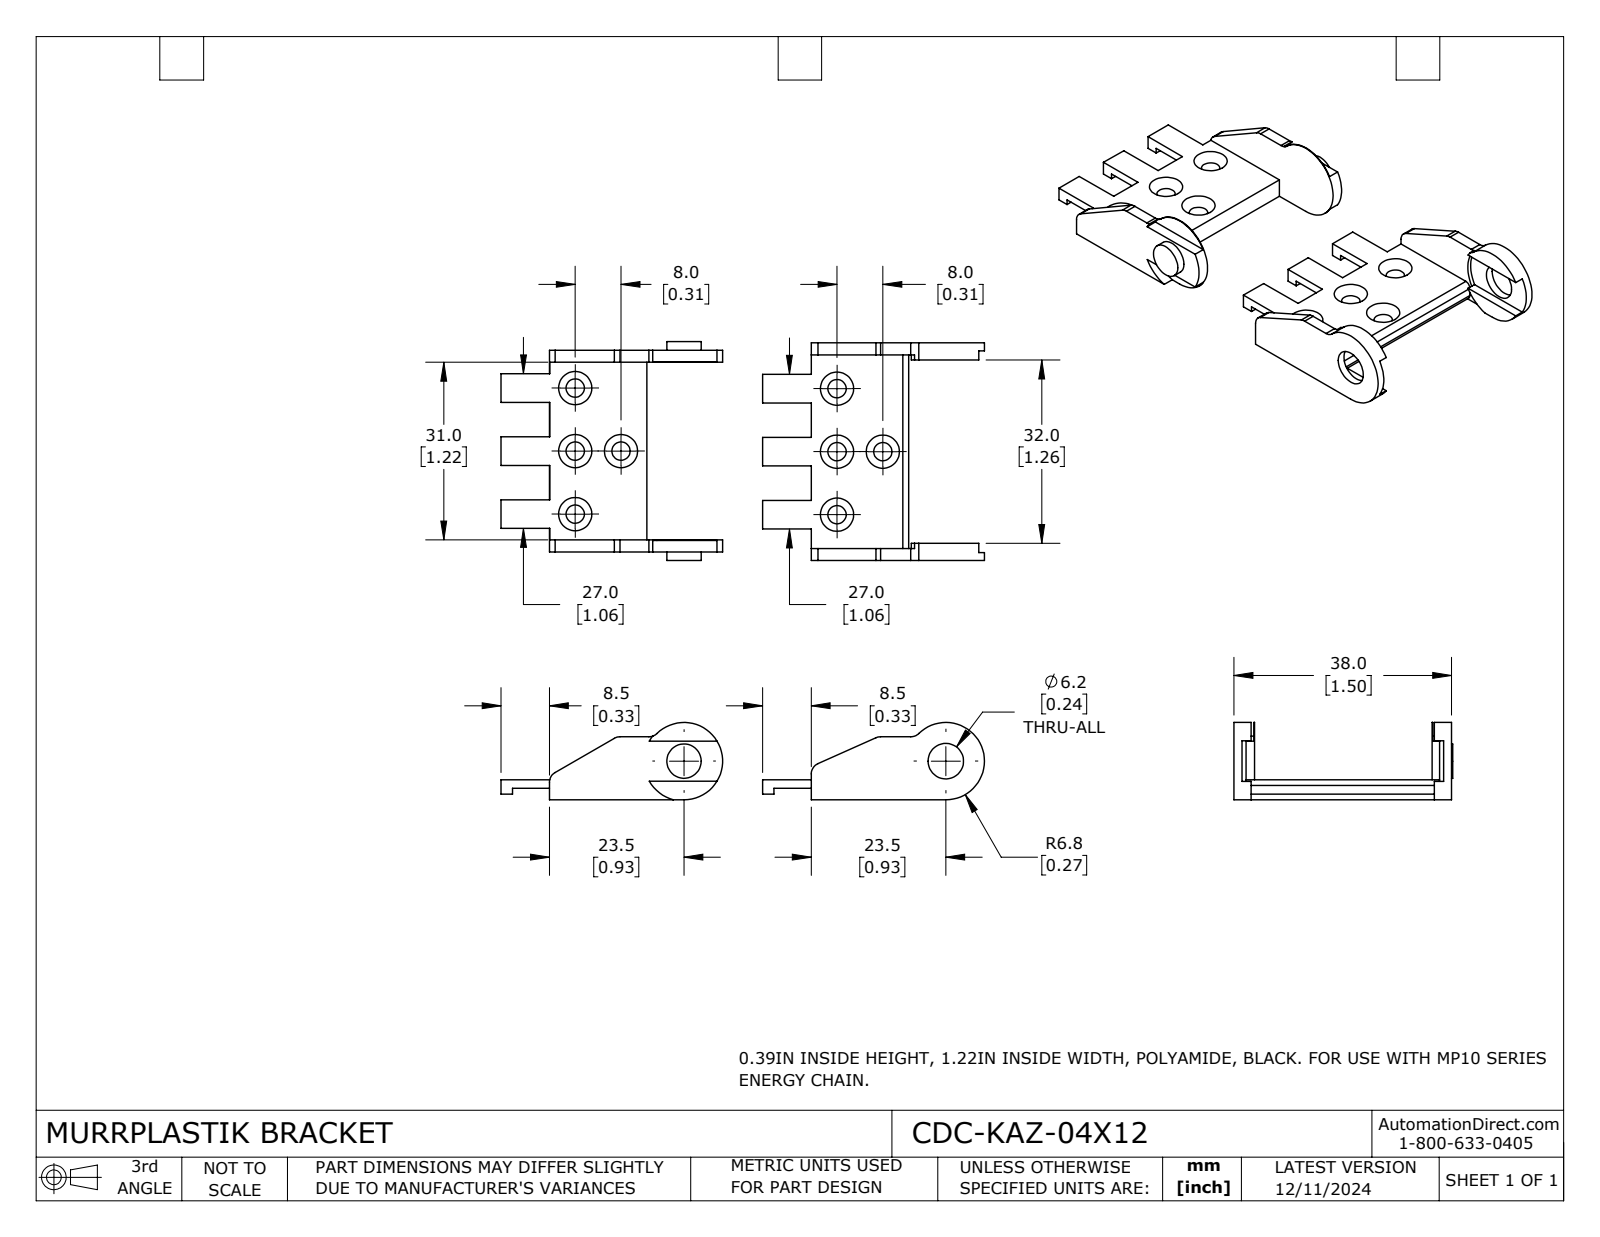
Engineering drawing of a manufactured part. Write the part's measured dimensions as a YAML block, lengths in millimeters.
part_name: "CDC-KAZ-04X12"
step_written_by: "SolidWorks 2024 (AUTOMOTIVE_DESIGN)"
units: millimeters
bodies: {solids: 2, faces: 130, planar: 80, cylindrical: 42, other: 8}
overall_size: [84.4, 38.2, 13.5]
volume: 6260
surface_area: 6452
round_holes:
  - {diameter: 3.2, count: 8}
  - {diameter: 6.2, count: 1}
round_bosses_or_shafts:
  - {diameter: 6, count: 1}
partial_cylinders:
  - {radius: 2, count: 6}
  - {radius: 1, count: 2}
  - {radius: 6.8, count: 2}
  - {radius: 7, count: 2}
face_to_face_distances: [3.5, 2.1, 1.5, 33.1, 2, 34.6, 34.4, 1.3, 35.2, 38]
hole_center_spacings: [11, 13.6, 45.7, 8, 22, 47, 47, 37.7]
